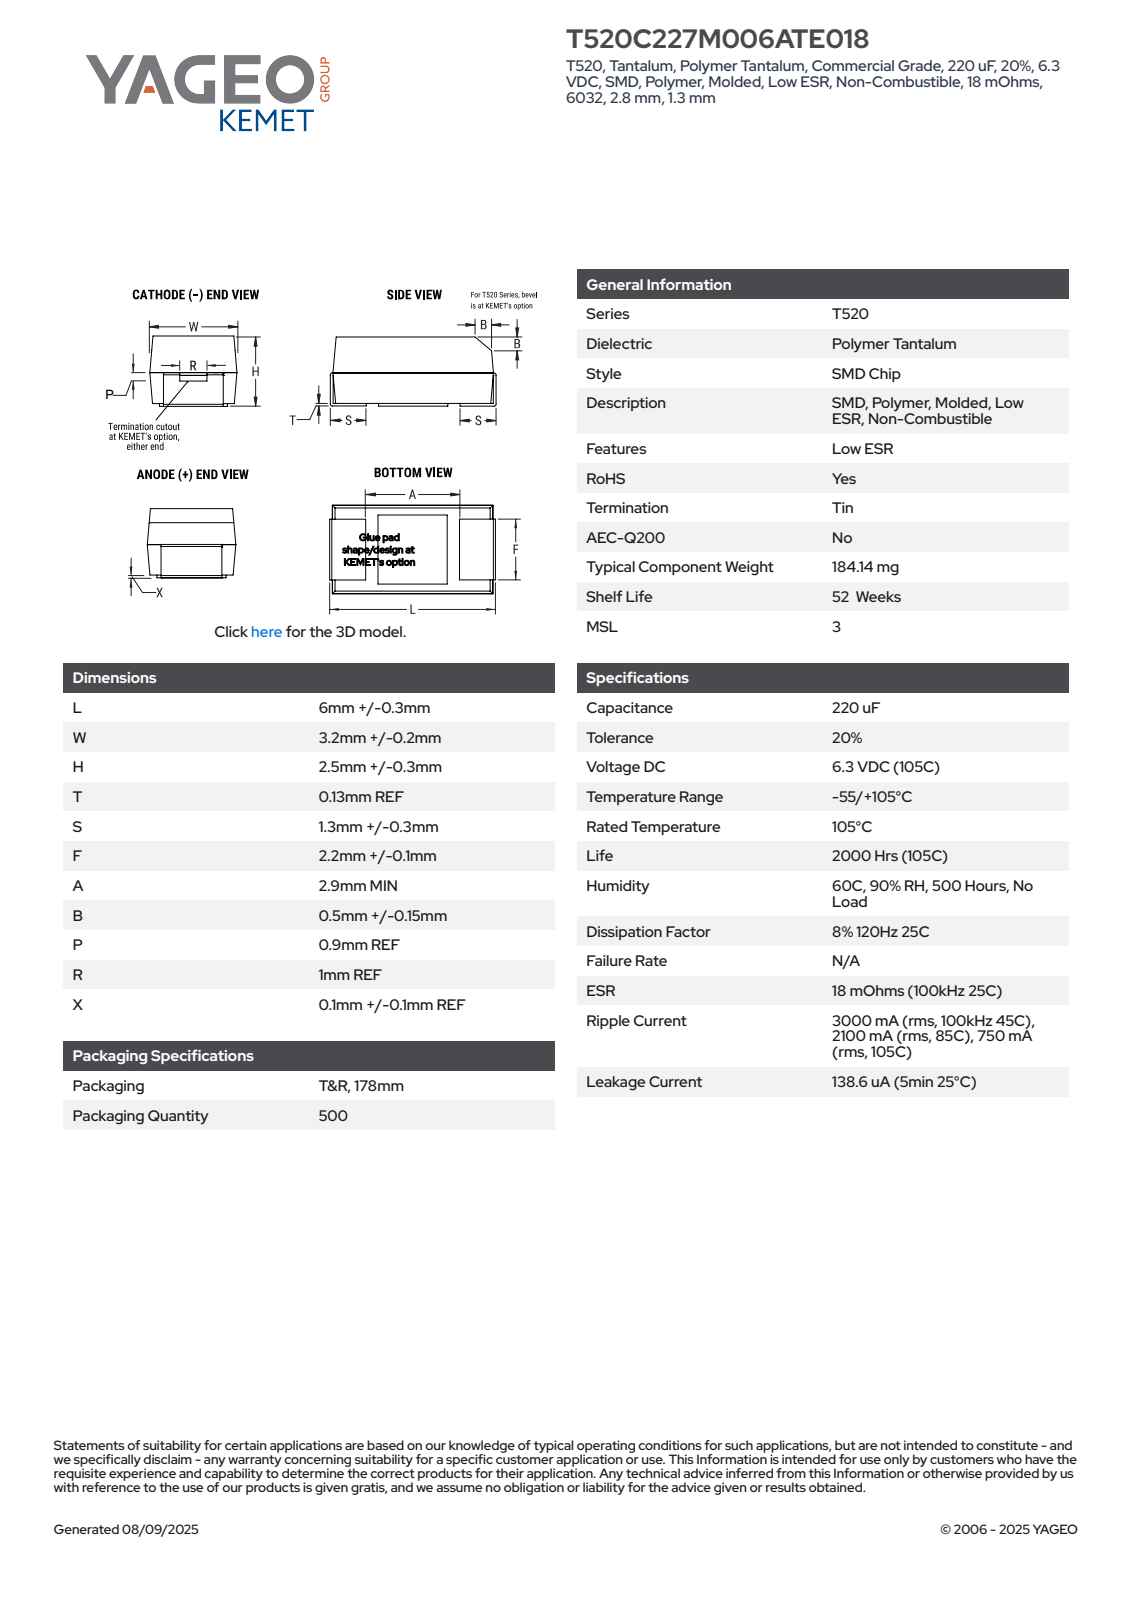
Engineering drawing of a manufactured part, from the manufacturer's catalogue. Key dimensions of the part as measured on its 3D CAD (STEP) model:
Part name (STEP PRODUCT): Case_Bottom_20; Case_Anode_20; CTS_6032_L6.30W3.50H2.80S1.3F2.2R1P0.9B0.5; Case_Cathode_20 (+1 more)
STEP written by: SolidWorks 2014 (AUTOMOTIVE_DESIGN)
Units: millimetres
Bodies: 4 solids, 43 faces (38 planar, 5 cylindrical, 0 other)
Overall size (bounding box): 6.3 × 3.5 × 2.8
Volume: 55 mm³ · Surface area: 154 mm²
Main face-to-face distances: 1.42, 1.25, 2.67, 3.48, 6.02, 1.35, 2.77, 1.38, 2.8, 6.17
